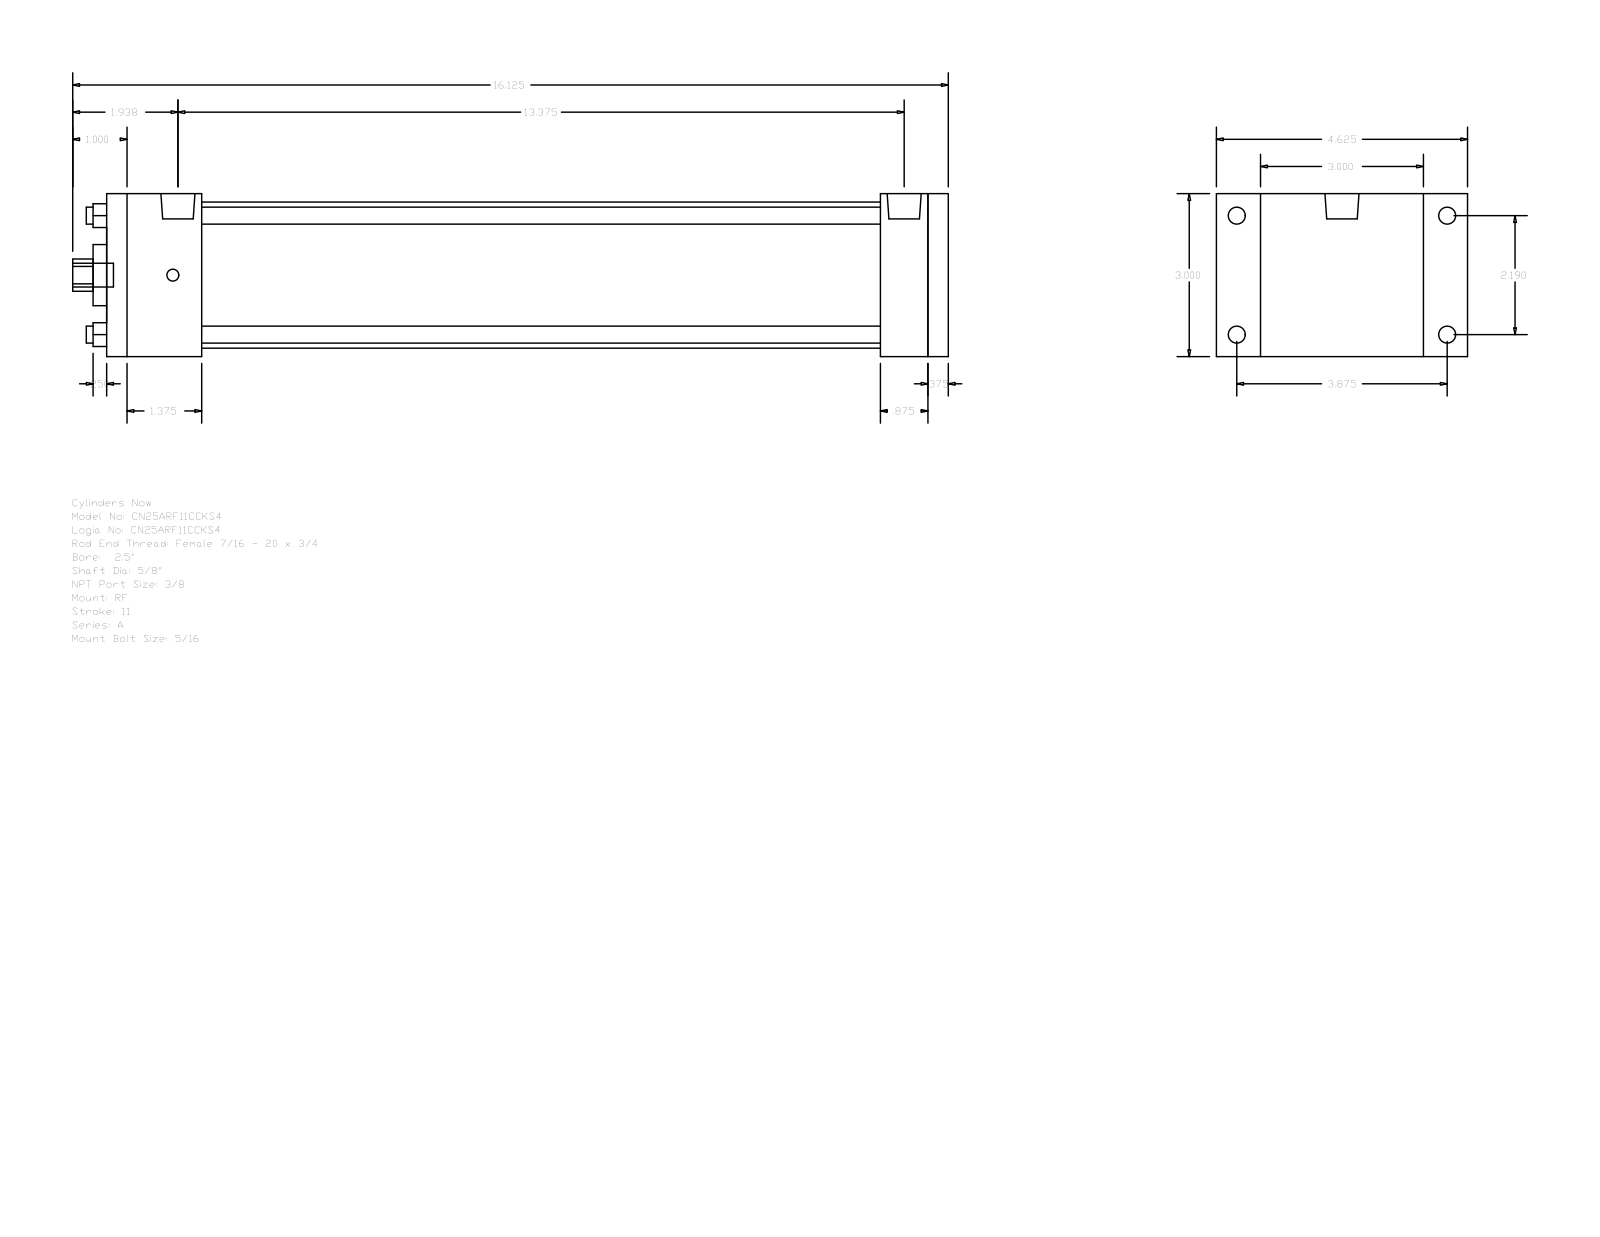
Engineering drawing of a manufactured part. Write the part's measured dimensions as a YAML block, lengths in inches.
part_name: "A_RF__0250_0.625"
step_written_by: "GSSL Pune (CONFIG_CONTROL_DESIGN)"
units: inches
bodies: {solids: 0, faces: 92, planar: 64, cylindrical: 28, other: 0}
overall_size: [16.125, 4.625, 3]
round_holes:
  - {diameter: 0.313, count: 4}
  - {diameter: 0.625, count: 1}
  - {diameter: 1.125, count: 1}
  - {diameter: 2.69, count: 1}
round_bosses_or_shafts:
  - {diameter: 0.313, count: 4}
  - {diameter: 0.219, count: 4}
  - {diameter: 0.627, count: 2}
  - {diameter: 0.437, count: 1}
partial_cylinders:
  - {radius: 0.297, count: 1}
face_to_face_distances: [3, 15.5, 0.375, 15.125, 1.75, 1.25, 14.25, 12.5, 13.375, 13.75]
hole_center_spacings: [1.548, 2.19, 3.097]
